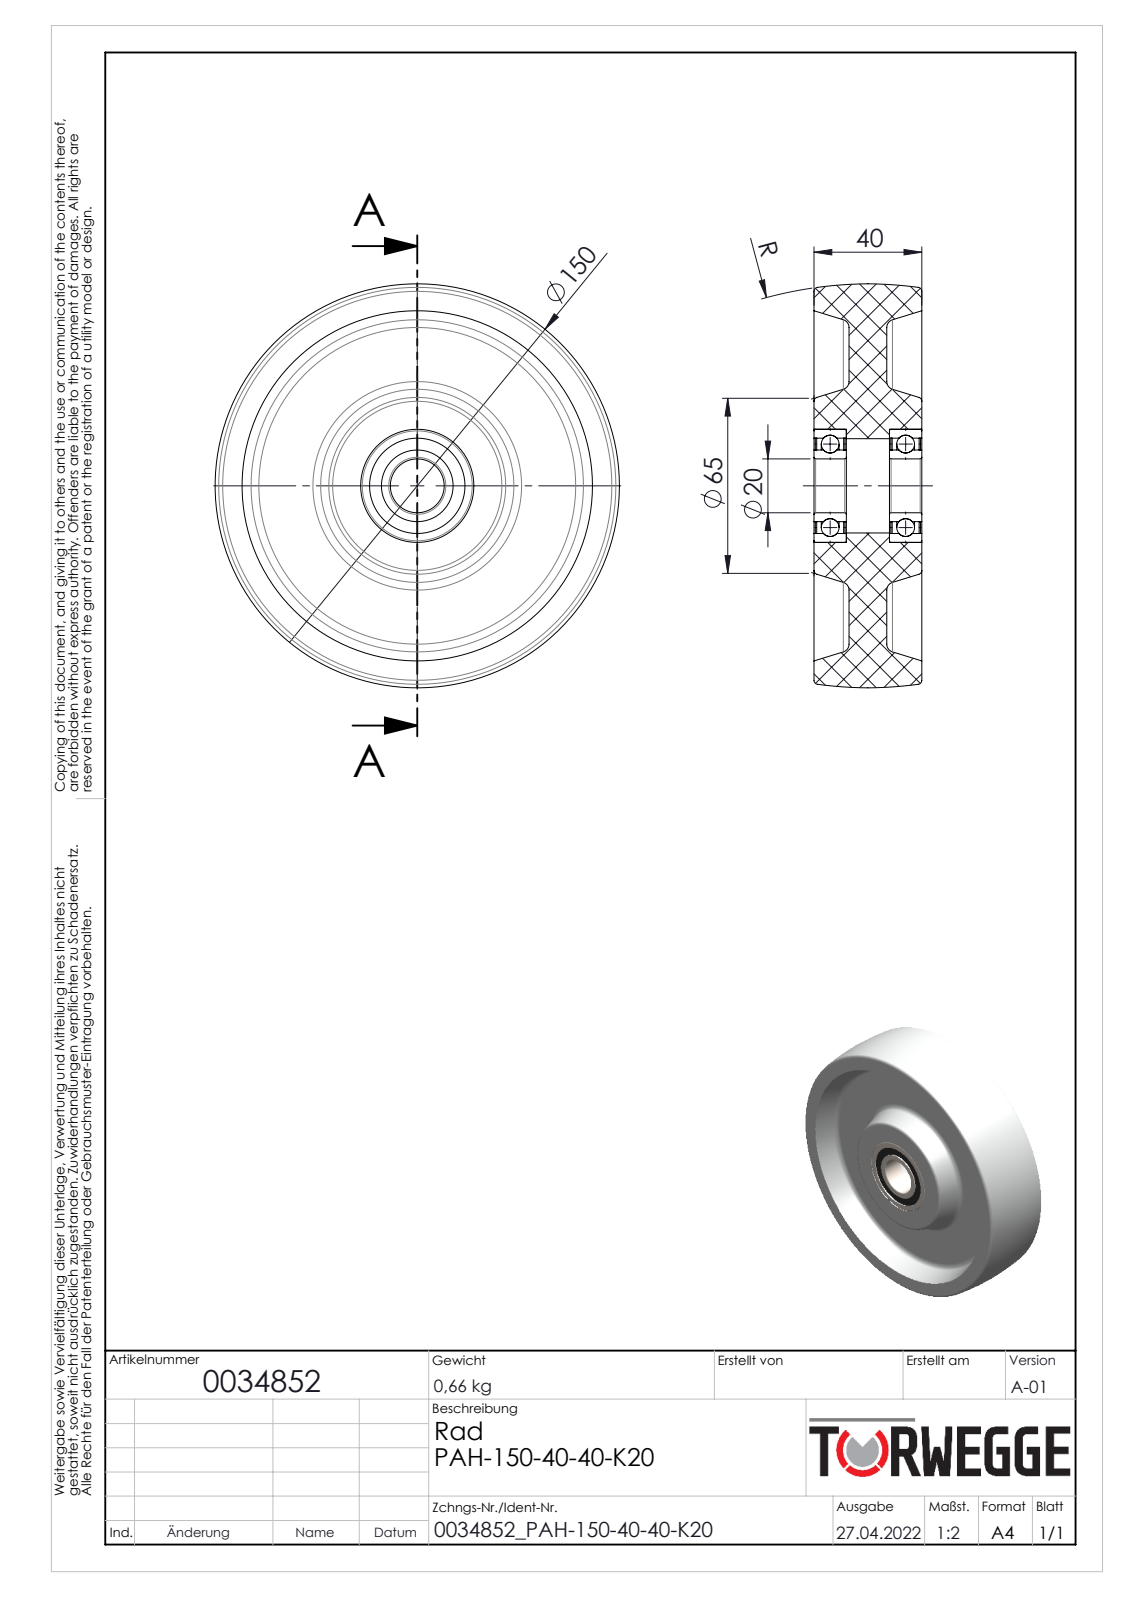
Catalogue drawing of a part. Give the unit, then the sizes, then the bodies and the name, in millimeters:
Units: millimetres
Overall size (bounding box): 150 × 150 × 40
Round holes (diameter × count): ⌀20 ×1, ⌀26.6 ×1, ⌀35 ×1, ⌀35.4 ×1, ⌀42 ×1
Main face-to-face distances: 27, 13, 14, 40, 1, 28, 0.5, 12, 11, 15
Volume: 443 481 mm³ · Surface area: 86 013 mm²
Bodies: 11 solids, 134 faces (24 planar, 46 cylindrical, 64 other)
Part name (STEP PRODUCT): 0034852
STEP written by: SolidWorks 2020 (AUTOMOTIVE_DESIGN)
